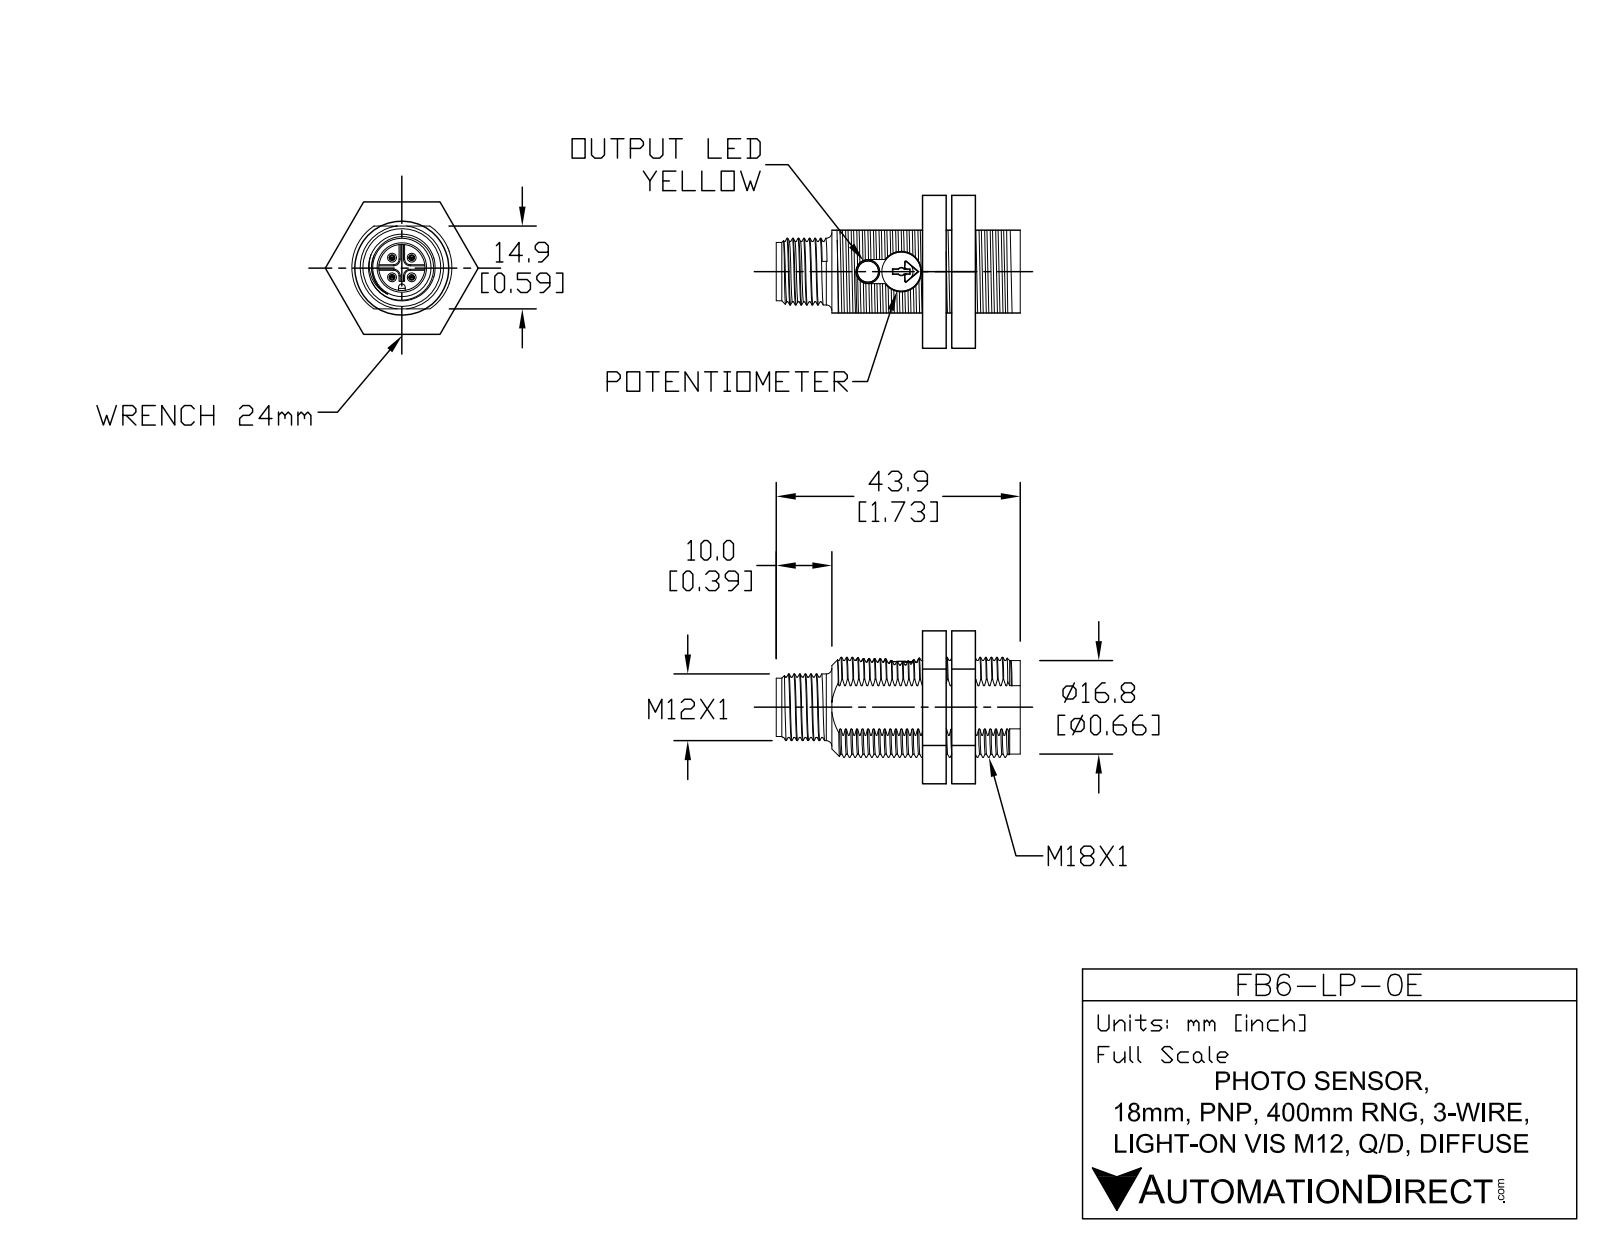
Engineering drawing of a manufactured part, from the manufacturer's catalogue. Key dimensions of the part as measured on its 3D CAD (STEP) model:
Part name (STEP PRODUCT): FB6-LP-0E
STEP written by: SolidWorks 2011 (AUTOMOTIVE_DESIGN)
Units: millimetres
Bodies: 7 solids, 226 faces (132 planar, 33 cylindrical, 61 other)
Overall size (bounding box): 43.9 × 27.69 × 24.57
Volume: 10 307 mm³ · Surface area: 5 165 mm²
Round holes (diameter × count): ⌀2.36 ×1, ⌀4.26 ×1, ⌀7.25 ×1, ⌀8.4 ×1
Round bosses / shafts (diameter × count): ⌀1 ×4, ⌀12 ×1, ⌀10.4 ×1
Partial cylindrical surfaces — rounded edges, fillets, slot ends (radius × count): R6.46 ×2, R7.46 ×2, R0.5 ×1, R0.65 ×1, R8.4 ×1, R8.5 ×1, R9 ×1
Main face-to-face distances: 8, 4.5, 24, 15, 1, 12.5, 3.5, 12.9, 13.9, 4.9
Hole centre spacings: 6.61
